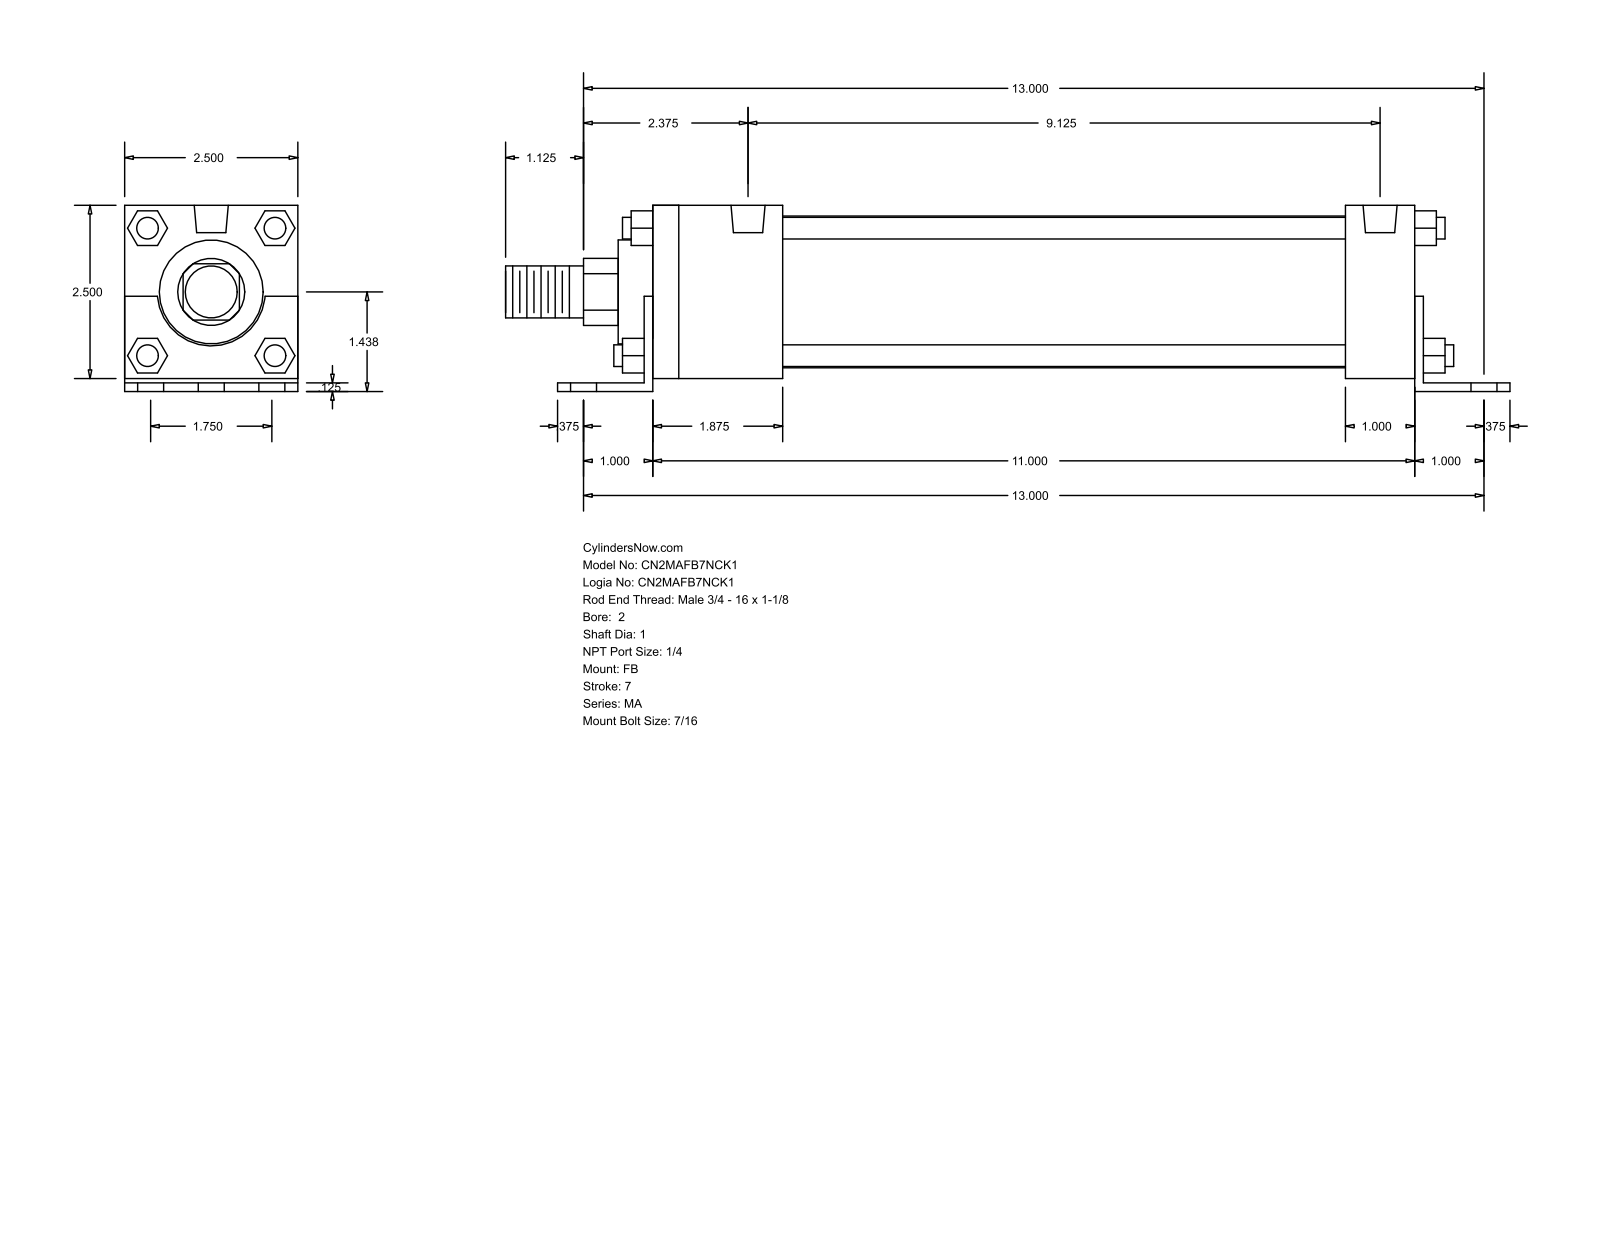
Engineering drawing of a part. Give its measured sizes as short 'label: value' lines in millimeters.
name: MA_FB__0200_1
written by: GSSL Pune (CONFIG_CONTROL_DESIGN)
unit: mm
bodies: 0 solids, 140 faces (105 planar, 35 cylindrical, 0 other)
size: 368.3 × 68.26 × 63.5
holes: 6× ⌀11.11, 4× ⌀7.94, 2× ⌀12.49
bosses: 4× ⌀7.94, 1× ⌀55.63, 1× ⌀38.1, 1× ⌀25.4, 1× ⌀19.05
rounds: 1× R12.29, 1× R19.81
face distances: 63.5, 3.17, 4.76, 68.26, 1.59, 65.09, 12.7, 3.18, 279.4, 282.58
hole spacings: 22.23, 330.95, 330.2, 44.11, 44.46, 64.3, 231.77, 270.78
